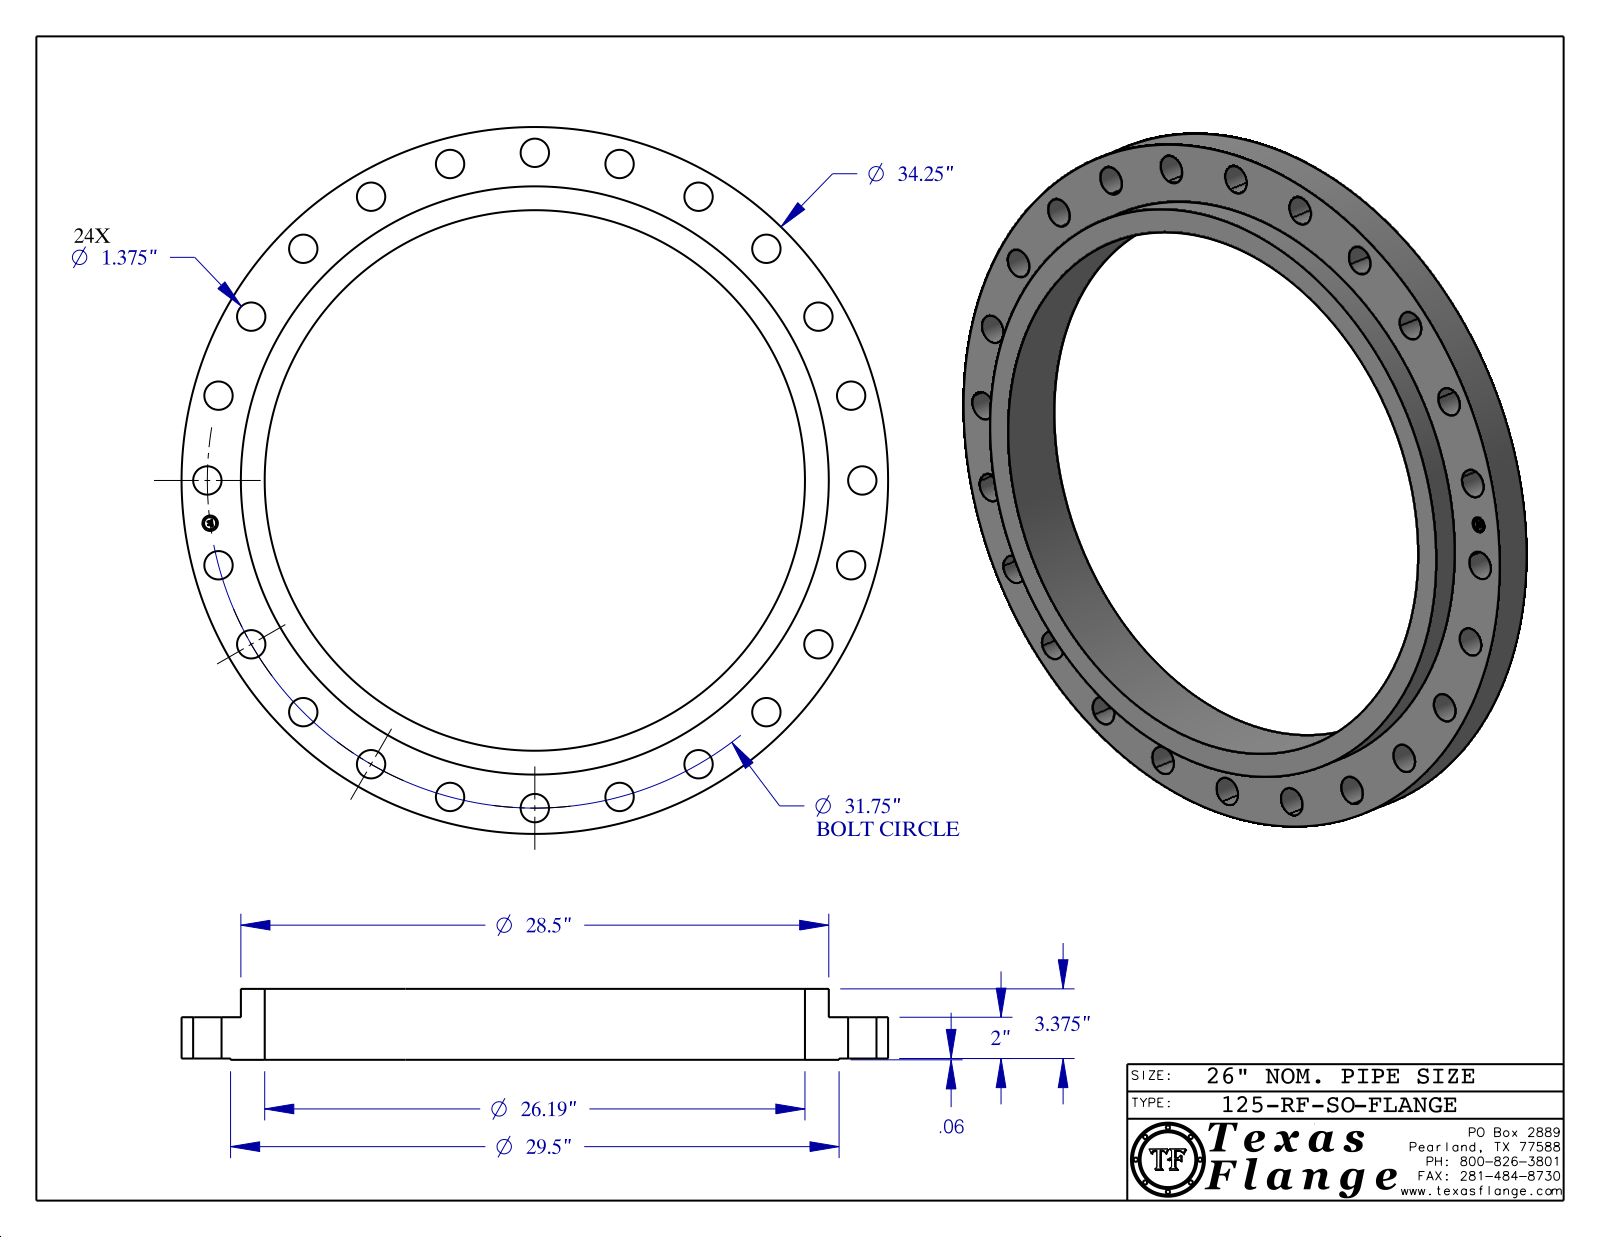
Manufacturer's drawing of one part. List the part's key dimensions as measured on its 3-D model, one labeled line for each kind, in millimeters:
Part name (STEP PRODUCT): 125-RF-SO-B16.1
STEP written by: CATIA V5 STEP AP214 (AUTOMOTIVE_DESIGN)
Units: millimetres
Bodies: 1 solid, 445 faces (369 planar, 76 cylindrical, 0 other)
Overall size (bounding box): 870 × 870 × 87.3
Volume: 13 760 000 mm³ · Surface area: 985 800 mm²
Round holes (diameter × count): ⌀34.9 ×24, ⌀19.1 ×1, ⌀665.2 ×1
Round bosses / shafts (diameter × count): ⌀1.1 ×8, ⌀870 ×1, ⌀749.3 ×1, ⌀723.9 ×1, ⌀15 ×1
Main face-to-face distances: 50.8, 1.6, 52.4, 87.3, 85.7, 34.9, 52, 50.4, 0.4, 35.3
Hole centre spacings: 403.2, 403.2, 745.1, 698.4, 105.3, 208.7, 308.6, 490.9
